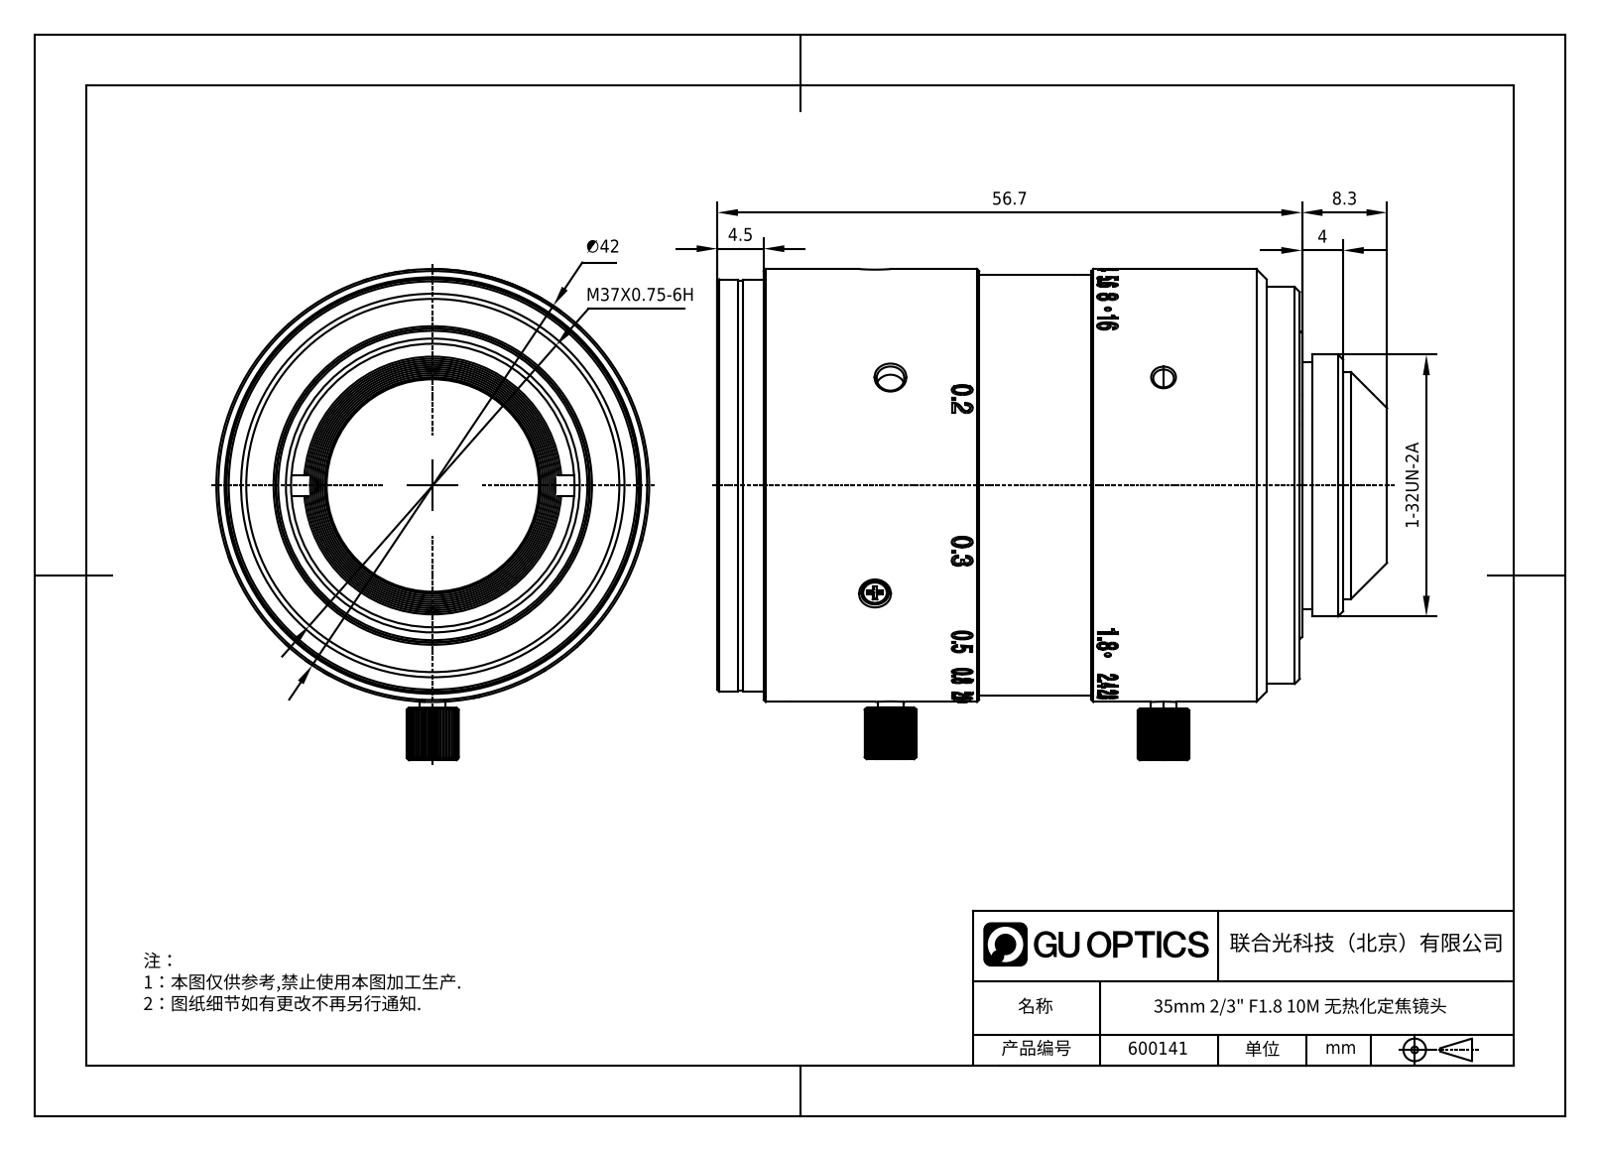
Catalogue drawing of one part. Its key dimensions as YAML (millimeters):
part_name: "MANIFOLD_SOLID_BREP_2024_1.stp; 600141.stp; DZ_LA3518A_2310-1-1_ASM_2_ASM.stp; 51A-615-0_1-0_05-0_025-0_01_5.stp (+8 more)"
step_written_by: "SolidWorks 2020 (CONFIG_CONTROL_DESIGN)"
units: millimeters
bodies: {solids: 23, faces: 2887, planar: 776, cylindrical: 677, other: 1434}
overall_size: [64.99, 47.65, 42]
volume: 39585
surface_area: 47353
round_holes:
  - {diameter: 1.3, count: 6}
  - {diameter: 2, count: 6}
  - {diameter: 2.7, count: 6}
  - {diameter: 1.1, count: 4}
  - {diameter: 1.5, count: 3}
  - {diameter: 1.8, count: 3}
  - {diameter: 3.2, count: 3}
  - {diameter: 4.9, count: 3}
  - {diameter: 1, count: 2}
  - {diameter: 10.5, count: 1}
  - {diameter: 12.1, count: 1}
  - {diameter: 12.58, count: 1}
round_bosses_or_shafts:
  - {diameter: 2.5, count: 7}
  - {diameter: 1.4, count: 5}
  - {diameter: 2.8, count: 3}
  - {diameter: 1.7, count: 3}
  - {diameter: 42, count: 1}
  - {diameter: 40.8, count: 1}
  - {diameter: 40, count: 1}
  - {diameter: 39.8, count: 1}
partial_cylinders:
  - {radius: 0.13, count: 22}
  - {radius: 1.5, count: 20}
  - {radius: 0.3, count: 18}
  - {radius: 0.5, count: 12}
  - {radius: 0.2, count: 6}
  - {radius: 0.75, count: 6}
  - {radius: 1.35, count: 6}
  - {radius: 1, count: 4}
face_to_face_distances: [2.63, 11.1, 2.73, 11, 13.73, 28.5, 13.63, 2.53, 9.3, 15.93]
hole_center_spacings: [1.5, 4.75, 7.95, 12.7, 13.8, 14.5, 15.3, 21.75]
